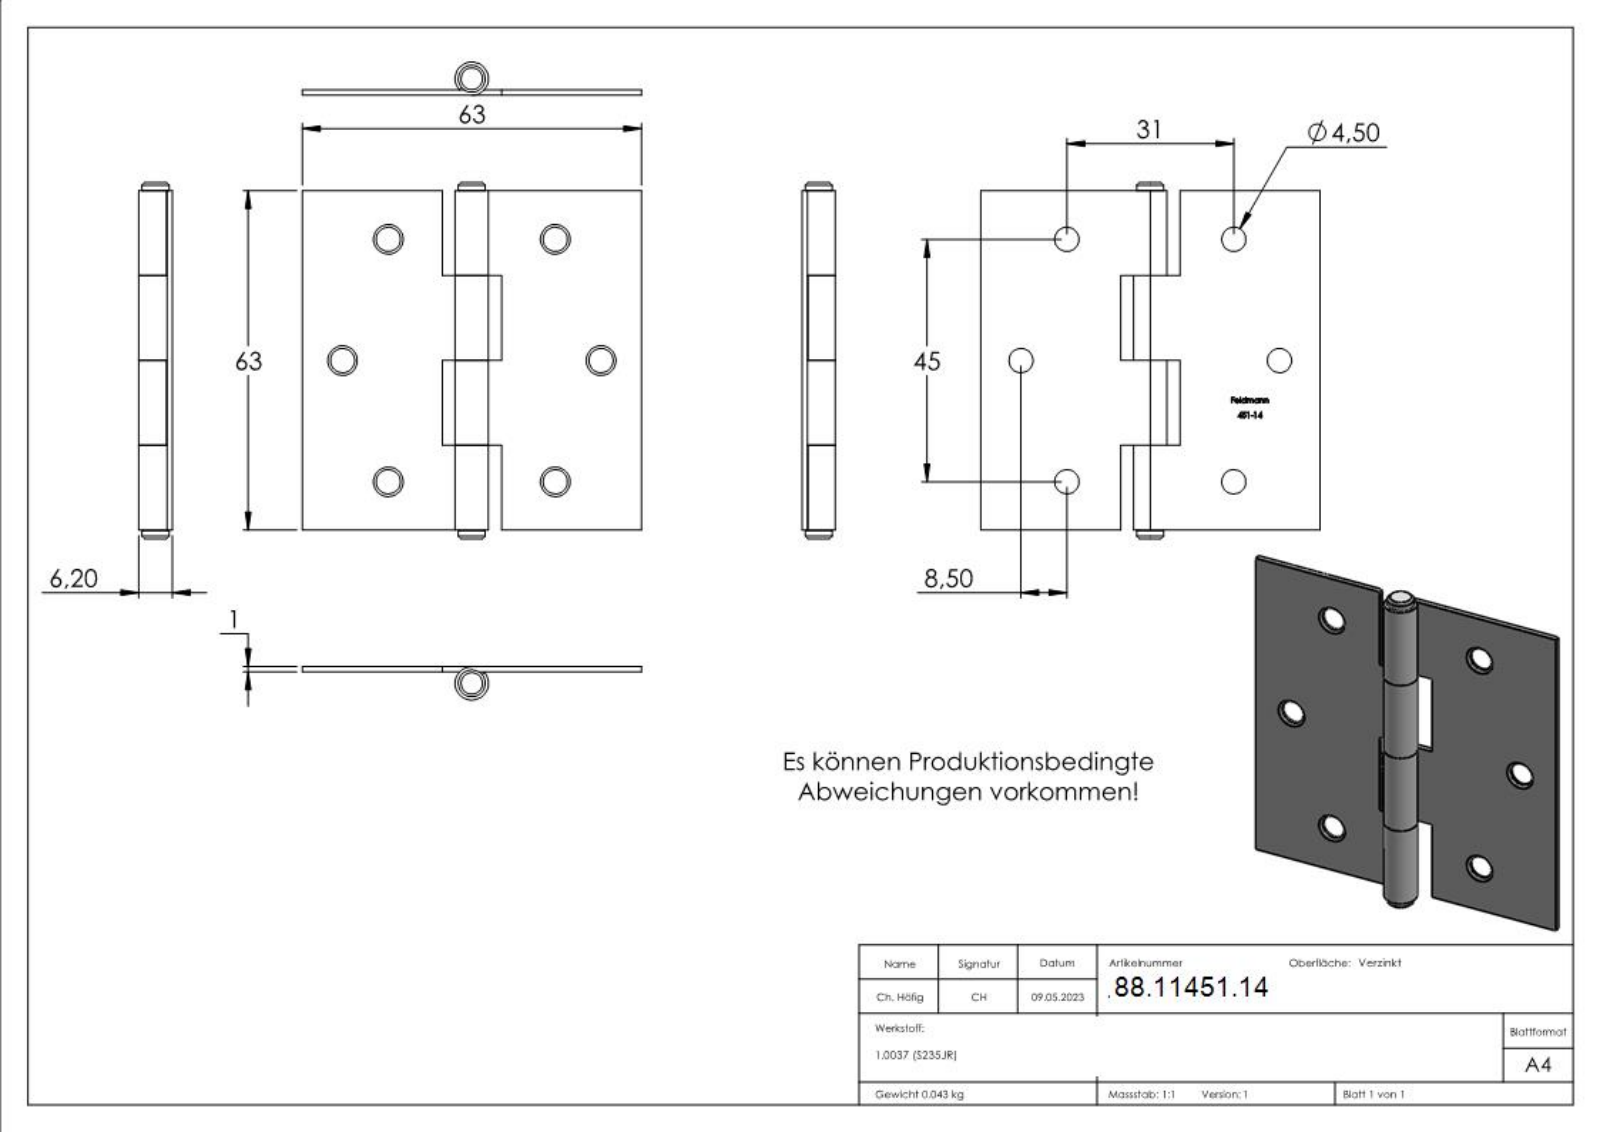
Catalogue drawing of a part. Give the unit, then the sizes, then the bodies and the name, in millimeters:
Units: millimetres
Overall size (bounding box): 66.1 × 63 × 6.2
Round holes (diameter × count): ⌀4.5 ×6, ⌀4.2 ×1
Round bosses / shafts (diameter × count): ⌀6.2 ×1, ⌀5 ×1, ⌀4.6 ×1
Main face-to-face distances: 1, 15.75, 63, 31.5, 47.25, 26, 37, 11, 1.55, 17.3
Hole centre spacings: 24.05, 45.46, 31, 45, 54.64, 48
Volume: 5 506 mm³ · Surface area: 10 397 mm²
Bodies: 3 solids, 230 faces (149 planar, 17 cylindrical, 64 other)
Part name (STEP PRODUCT): 451-14 Teil3; 451-14 Teil2; 451-14 Teil1; 451-14
STEP written by: SolidWorks 2018 (CONFIG_CONTROL_DESIGN)
